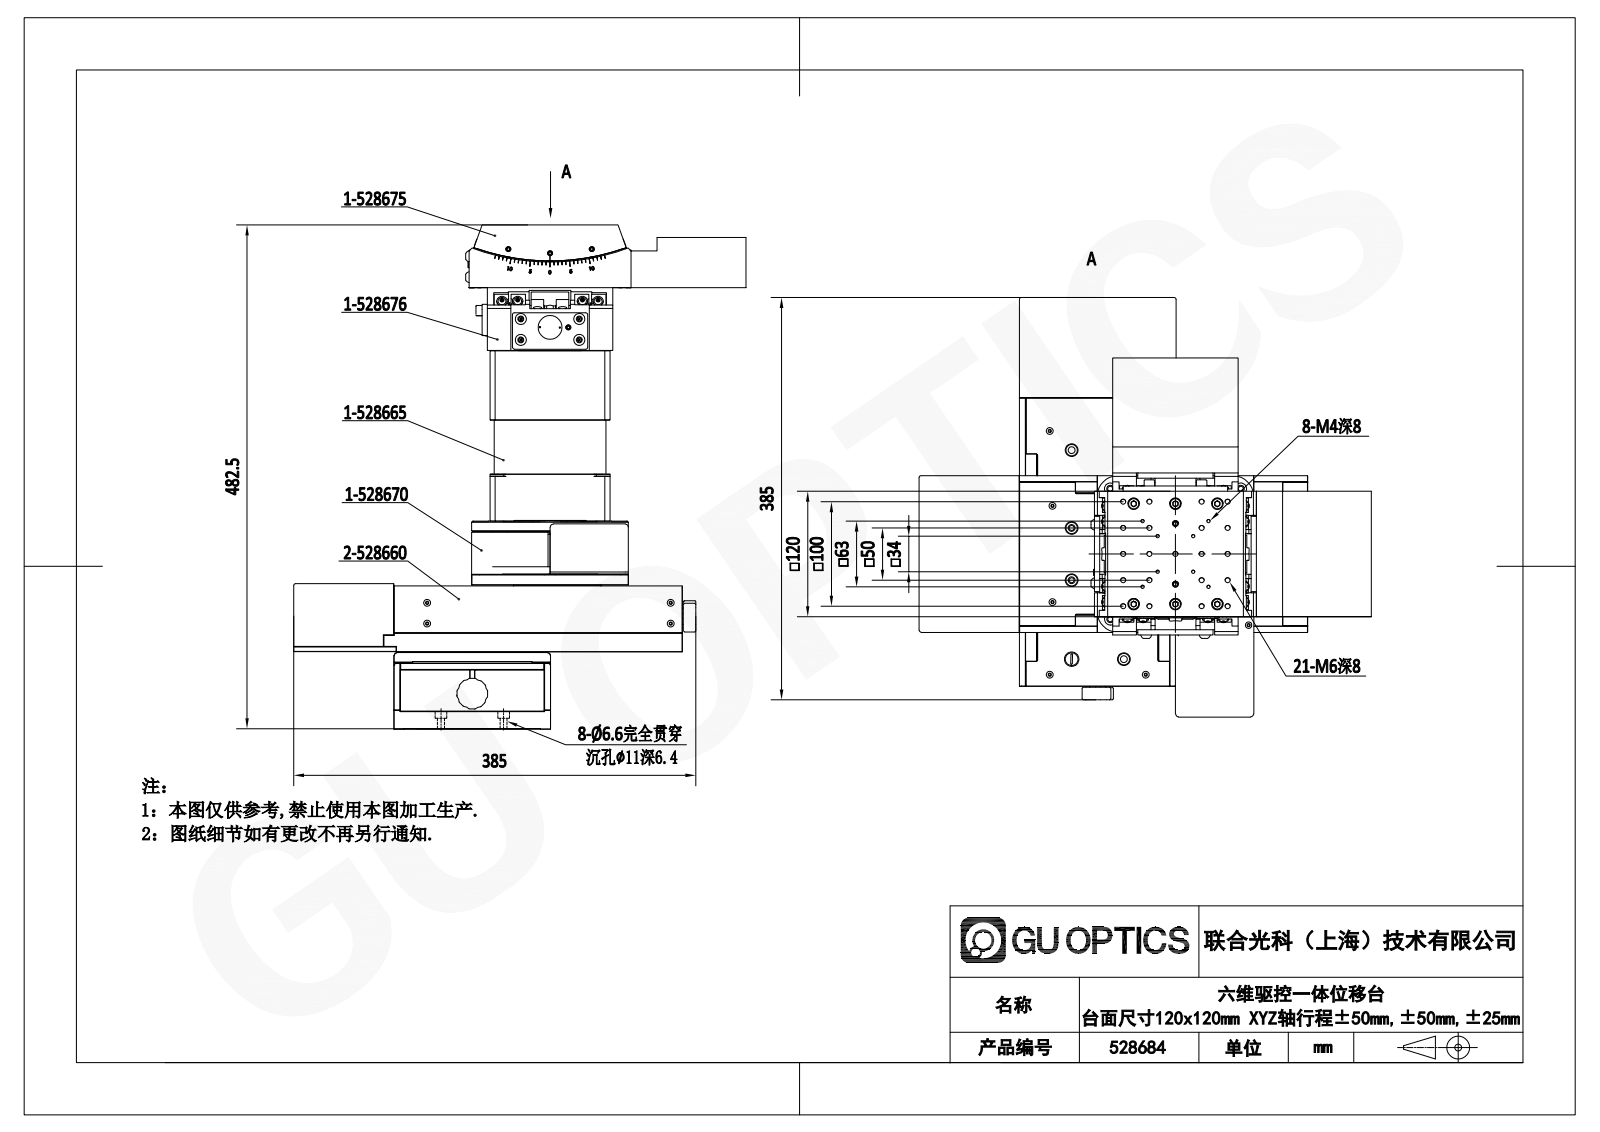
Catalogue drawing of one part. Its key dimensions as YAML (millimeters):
part_name: "528684; 528676; 528665; 528660 (+2 more)"
step_written_by: "SolidWorks 2020 (CONFIG_CONTROL_DESIGN)"
units: millimeters
bodies: {solids: 263, faces: 10762, planar: 6675, cylindrical: 2316, other: 1771}
overall_size: [482.5, 432.94, 401.44]
volume: 8371000
surface_area: 2444000
round_holes:
  - {diameter: 5, count: 187}
  - {diameter: 3.3, count: 107}
  - {diameter: 2.5, count: 104}
  - {diameter: 3.4, count: 82}
  - {diameter: 6.5, count: 77}
  - {diameter: 11, count: 59}
  - {diameter: 8, count: 48}
  - {diameter: 6.6, count: 39}
  - {diameter: 3.5, count: 32}
  - {diameter: 6, count: 29}
  - {diameter: 2.46, count: 24}
  - {diameter: 9.5, count: 24}
round_bosses_or_shafts:
  - {diameter: 4, count: 44}
  - {diameter: 6, count: 35}
  - {diameter: 10, count: 32}
  - {diameter: 7, count: 24}
  - {diameter: 9.5, count: 8}
  - {diameter: 8.5, count: 8}
  - {diameter: 2.5, count: 8}
  - {diameter: 5, count: 7}
partial_cylinders:
  - {radius: 5, count: 101}
  - {radius: 1, count: 73}
  - {radius: 2, count: 59}
  - {radius: 0.3, count: 36}
  - {radius: 3.5, count: 20}
  - {radius: 3, count: 19}
  - {radius: 7.5, count: 18}
  - {radius: 1.5, count: 12}
face_to_face_distances: [74, 17.5, 56.5, 6, 4, 16.5, 62.5, 2.5, 107, 10.5]
hole_center_spacings: [16, 20, 15, 18.35, 25, 33.03, 33.33, 40]
